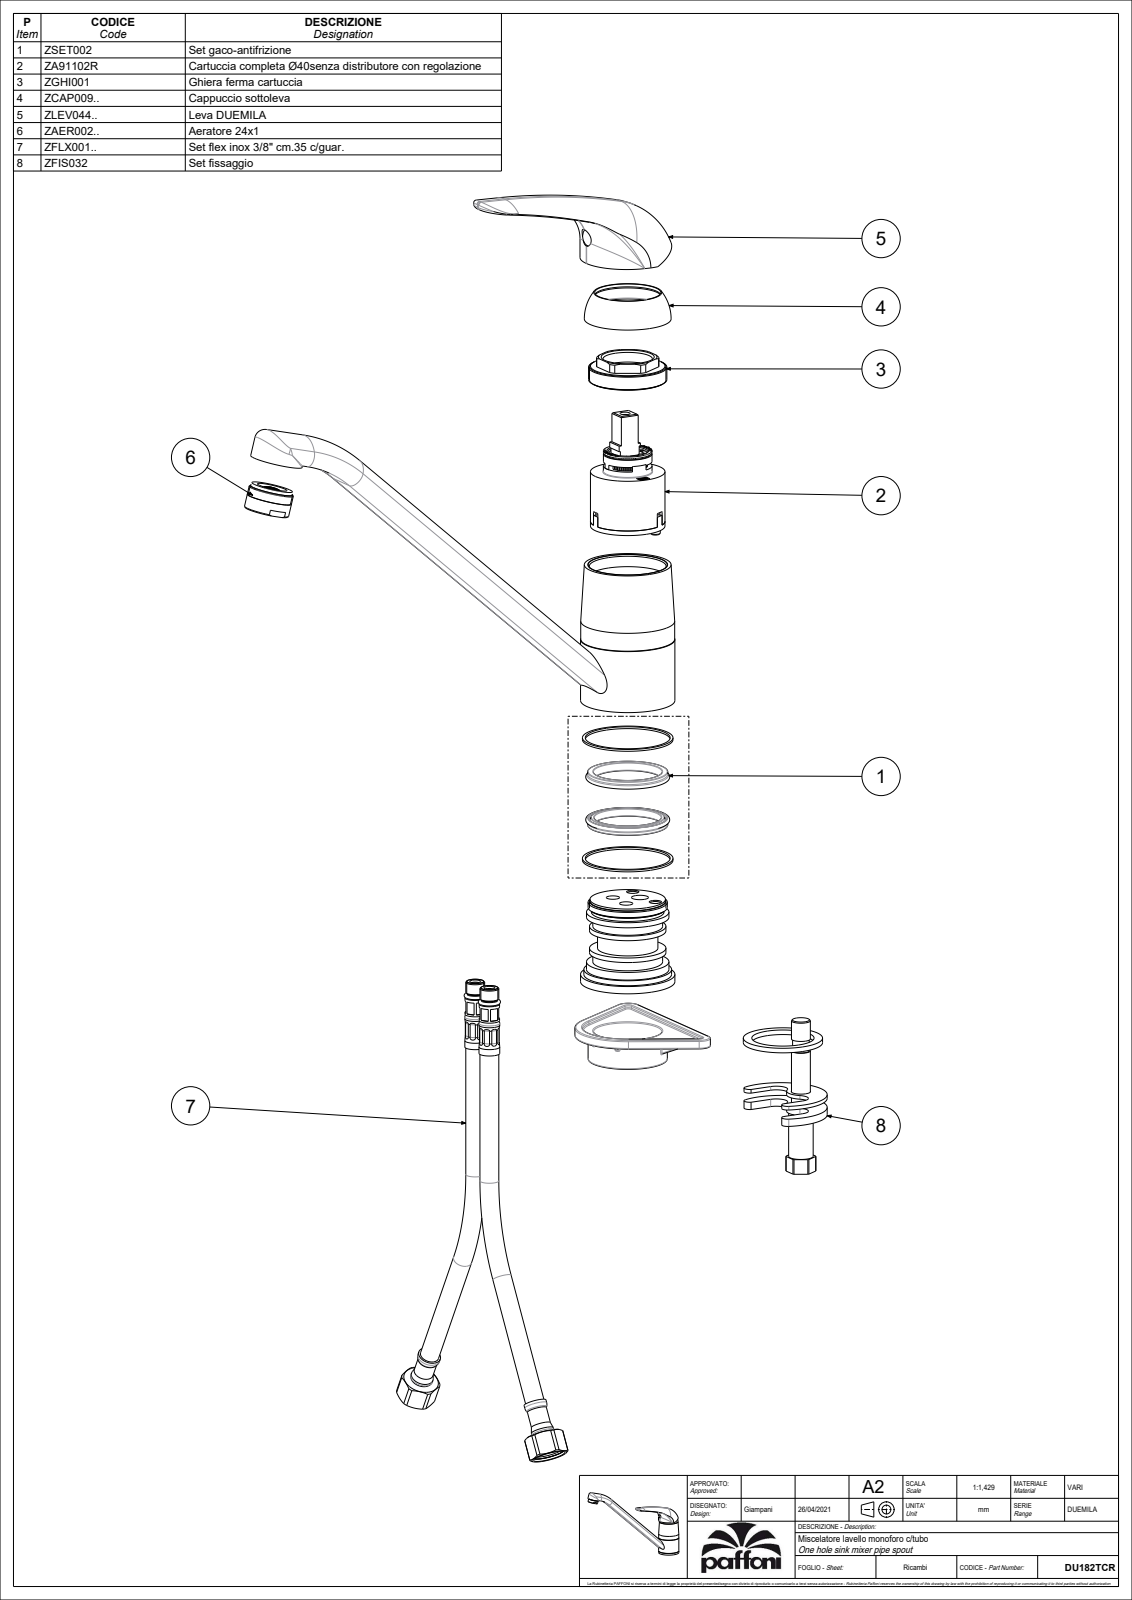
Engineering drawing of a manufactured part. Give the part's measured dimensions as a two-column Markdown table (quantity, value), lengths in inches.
| quantity | value |
| --- | --- |
| part name | DU182TCR |
| STEP written by | CREO PARAMETRIC BY PTC INC, 2020044 (CONFIG_CONTROL_DESIGN) |
| units | inches |
| bodies | 2 solids, 237 faces (50 planar, 101 cylindrical, 86 other) |
| overall size | 9.981 × 7.18 × 1.969 |
| volume | 12.75 in³ |
| surface area | 121.4 in² |
| round holes (diameter × count) | 0.354 × 5, 0.217 × 2, 0.276 × 2, 0.433 × 2, 0.362 × 1, 0.364 × 1, 1.378 × 1, 1.602 × 1, 1.61 × 1, 1.732 × 1, 1.748 × 1, 1.87 × 1 |
| round bosses / shafts (diameter × count) | 1.969 × 1, 1.961 × 1, 1.831 × 1, 1.764 × 1, 1.72 × 1, 1.594 × 1, 1.575 × 1, 1.457 × 1 |
| partial cylindrical surfaces (radius × count) | 0.217 × 4, 0.059 × 2, 0.591 × 2, 0.65 × 2, 0.945 × 2, 0.965 × 2, 0.709 × 1, 0.981 × 1 |
| main face-to-face distances | 3.676, 0.051, 0.05, 0.295, 1.78, 1.778, 1.728, 0.768, 0.098, 0.669 |
| hole center spacings | 0.044, 0.335, 0.339, 0.474, 0.483, 0.541, 0.564, 0.572 |
